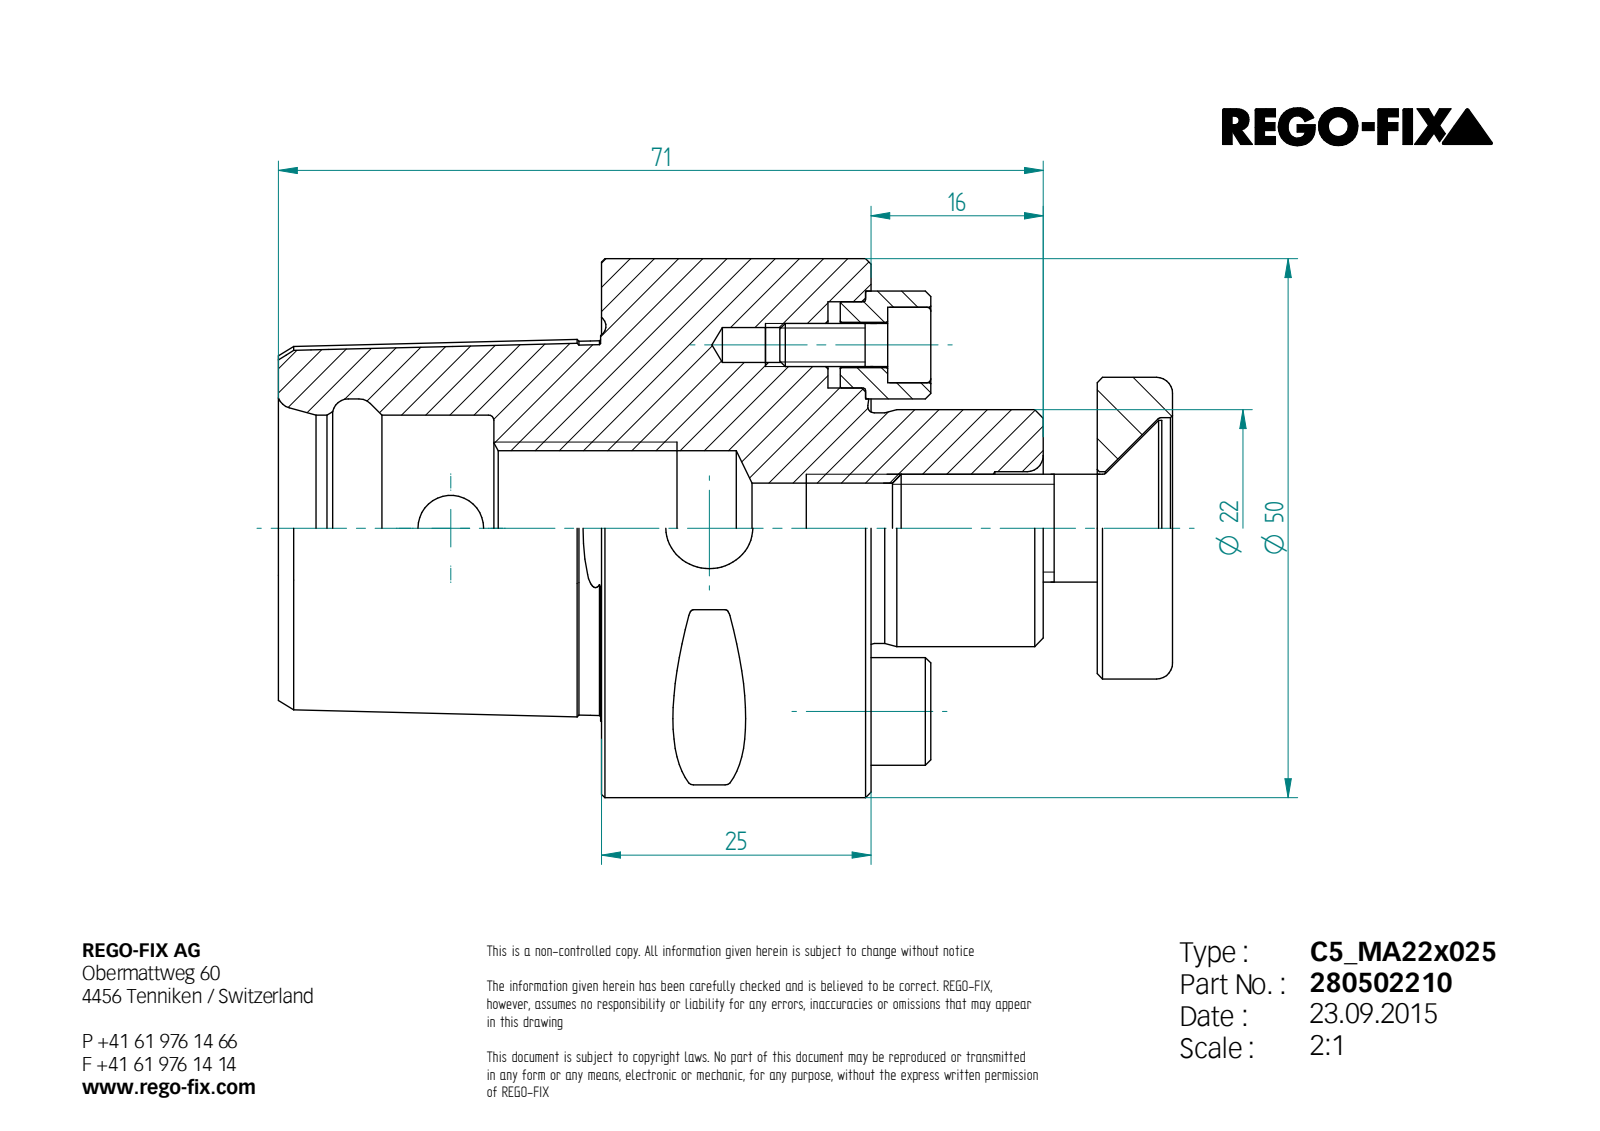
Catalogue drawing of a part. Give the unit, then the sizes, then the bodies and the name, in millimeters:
Units: millimetres
Overall size (bounding box): 83 × 50 × 50
Round holes (diameter × count): ⌀3.22 ×2, ⌀3.24 ×2, ⌀4.2 ×2, ⌀7 ×2, ⌀8 ×2, ⌀10 ×2, ⌀4 ×1, ⌀6.1 ×1, ⌀8.38 ×1, ⌀10.5 ×1, ⌀14.38 ×1, ⌀20.5 ×1
Round bosses / shafts (diameter × count): ⌀4 ×2, ⌀50 ×1, ⌀28 ×1, ⌀22 ×1, ⌀21.4 ×1, ⌀20 ×1, ⌀10 ×1
Partial cylindrical surfaces — rounded edges, fillets, slot ends (radius × count): R0.5 ×8, R4 ×1
Main face-to-face distances: 25, 21, 46, 6, 27, 30, 55, 76, 52, 82
Hole centre spacings: 17, 26, 34
Volume: 73 934 mm³ · Surface area: 20 611 mm²
Bodies: 7 solids, 212 faces (67 planar, 51 cylindrical, 94 other)
Part name (STEP PRODUCT): 0003451; 0003387; 0010452; 0010451 (+1 more)
STEP written by: Unknown (AUTOMOTIVE_DESIGN)
